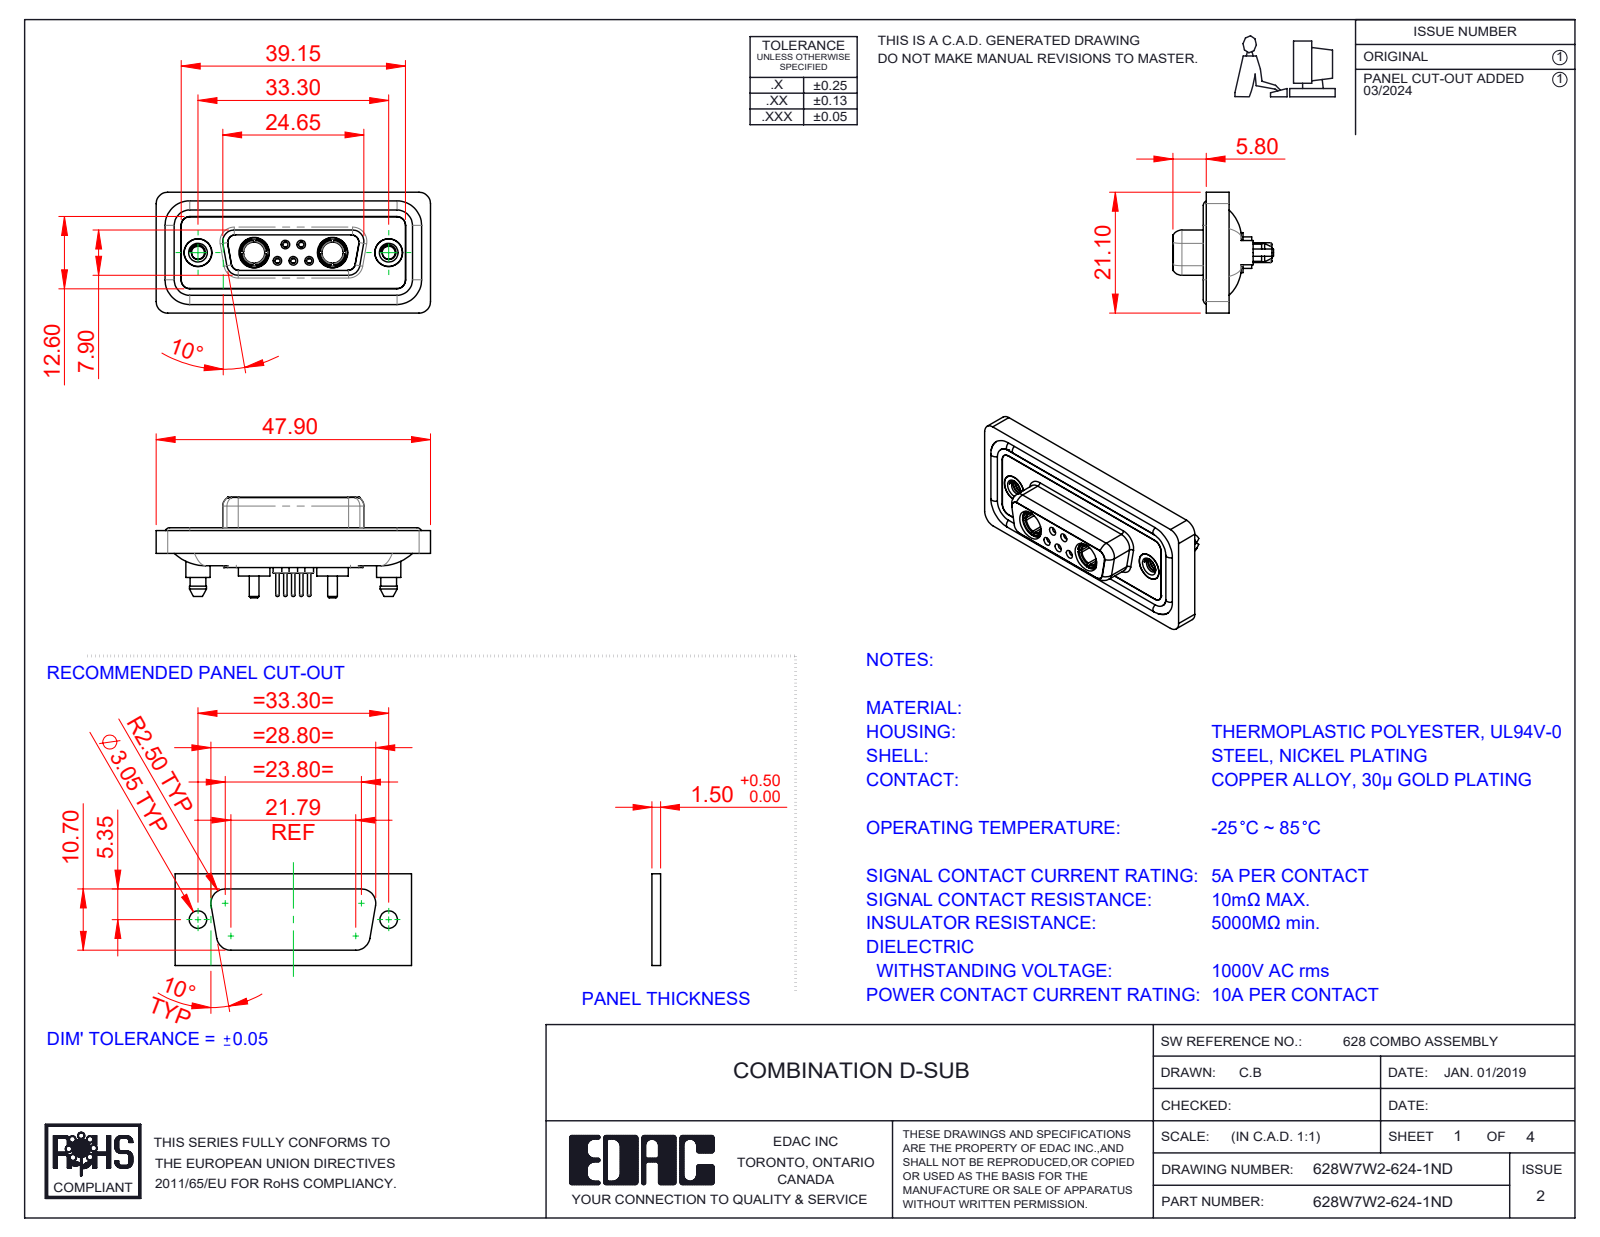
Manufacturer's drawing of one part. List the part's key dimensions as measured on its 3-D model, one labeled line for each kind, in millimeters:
Part name (STEP PRODUCT): 628Combo Shell Front_15 Contacts; 628Combo Contact Row 1_24; 628W7W2-624-1ND; 628Combo Waterproof Housing_15 Contacts (+5 more)
STEP written by: SolidWorks 2023 (CONFIG_CONTROL_DESIGN)
Units: millimetres
Bodies: 16 solids, 875 faces (254 planar, 377 cylindrical, 244 other)
Overall size (bounding box): 47.9 × 21.1 × 17.55
Volume: 6 183 mm³ · Surface area: 10 199 mm²
Round holes (diameter × count): ⌀0.9 ×5, ⌀1.1 ×5, ⌀1.5 ×5, ⌀2 ×5, ⌀4.85 ×4, ⌀1.6 ×3, ⌀1.7 ×2, ⌀2.26 ×2, ⌀3.7 ×2, ⌀4 ×2, ⌀4.05 ×2, ⌀5 ×2
Round bosses / shafts (diameter × count): ⌀1.6 ×6, ⌀2.2 ×5, ⌀0.6 ×5, ⌀5.5 ×2, ⌀5.4 ×2, ⌀5.2 ×2, ⌀4.96 ×2, ⌀4.95 ×2
Partial cylindrical surfaces — rounded edges, fillets, slot ends (radius × count): R1.5 ×24, R2 ×20, R1.35 ×12, R1.6 ×10, R0.25 ×4, R0.5 ×4, R0.6 ×4, R0.65 ×4
Main face-to-face distances: 0.4, 1.8, 1.6, 0.5, 2.9, 1.1, 7.45, 5.65, 6.6, 7.05
Hole centre spacings: 3.16, 2.77, 9.8, 23.5, 4.31, 4.33, 5.03, 5.04
